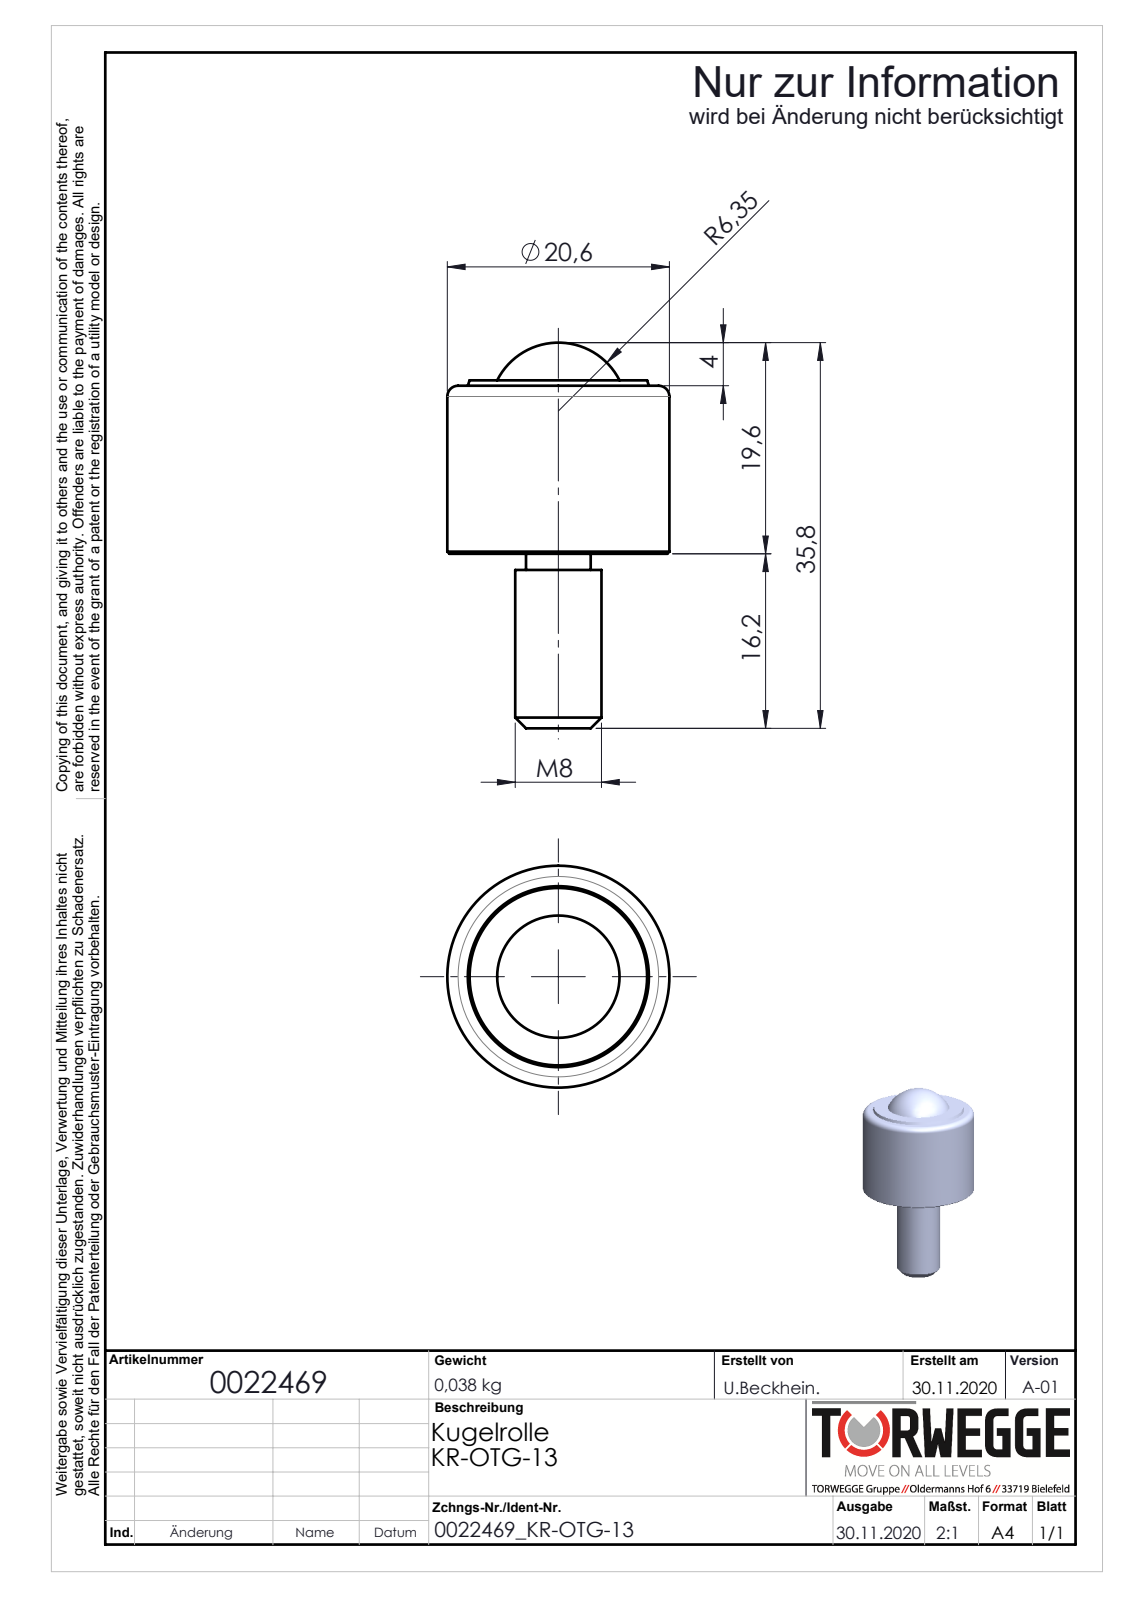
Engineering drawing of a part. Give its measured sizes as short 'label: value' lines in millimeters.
name: 0022469
written by: SolidWorks 2018 (AUTOMOTIVE_DESIGN)
unit: mm
bodies: 1 solid, 20 faces (5 planar, 6 cylindrical, 9 other)
size: 35.8 × 20.6 × 20.6
volume: 6 262 mm³; area: 2 123 mm²
bosses: 1× ⌀20.6, 1× ⌀8, 1× ⌀6
face distances: 16.1, 15.6, 0.5, 16.2, 31.8, 32.3, 14.7, 1.5, 17.1, 17.6
